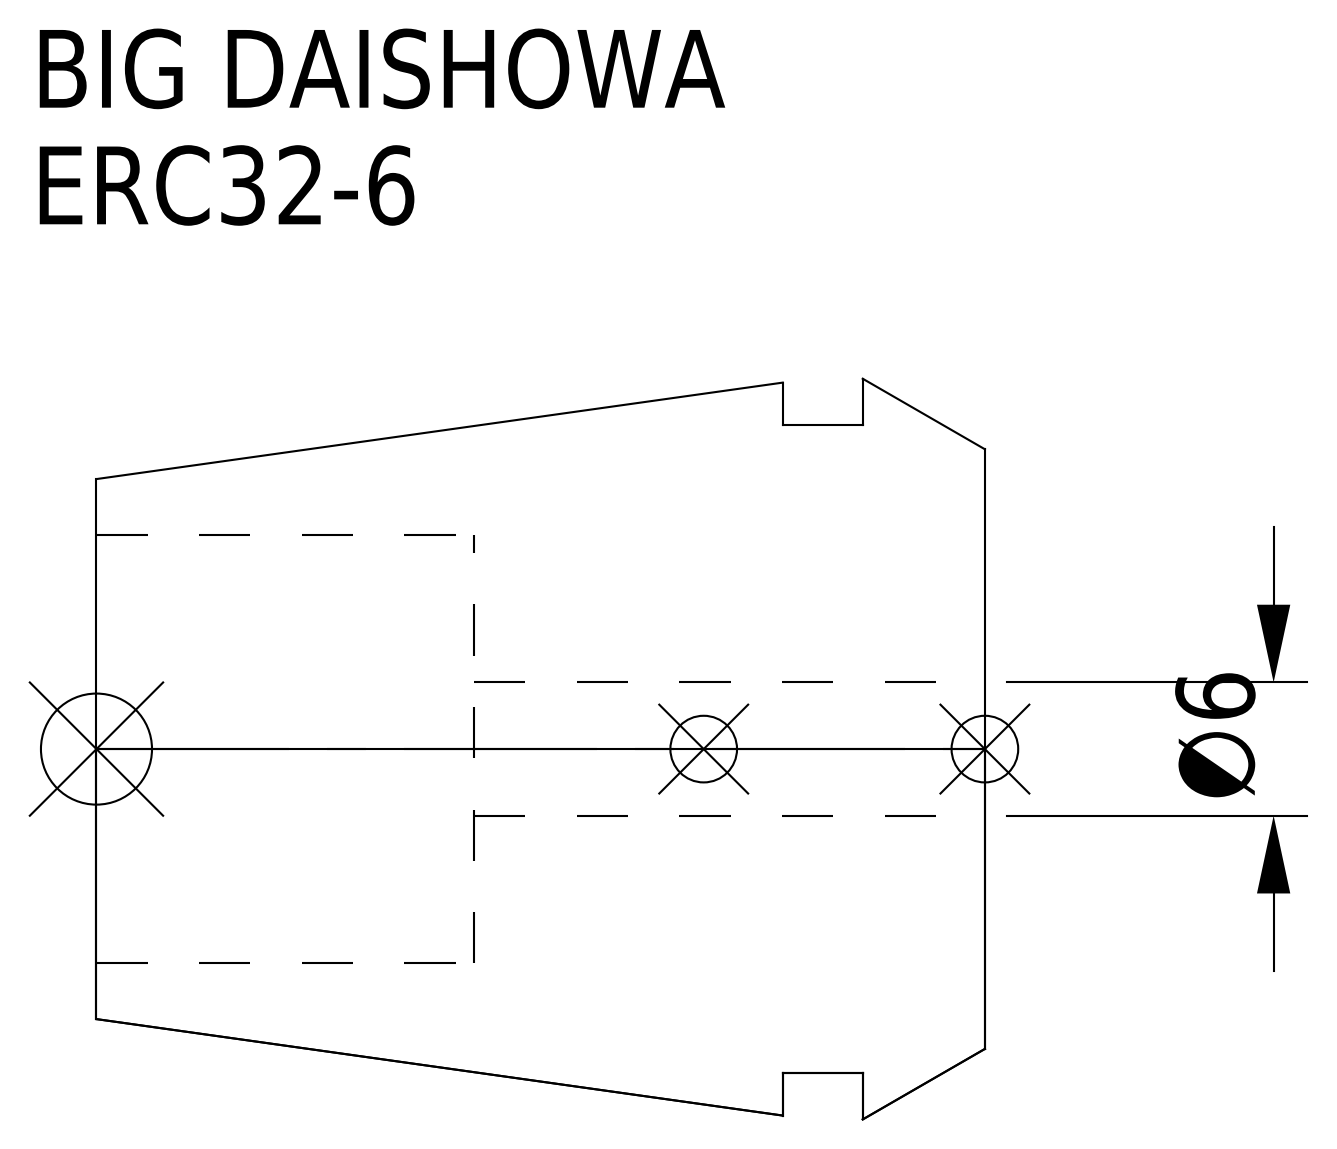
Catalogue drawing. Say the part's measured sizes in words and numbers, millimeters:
The part is named "ERC32-6". Its 3-D file was written by "CREO PARAMETRIC BY PTC INC, 2016380 (AUTOMOTIVE_DESIGN)". It is 1 solid with 15 faces: 5 planar, 6 cylindrical and 4 other. Overall it measures 40 by 33.35 by 33.35 millimeters. Its volume is 20 819 cubic millimeters and its surface area 6 576 square millimeters. Round holes: 1 of diameter 6, 1 of diameter 19.3. Round bosses or shafts: 1 of diameter 29.2. The main face-to-face distances are 23, 5.5, 17.5, 9.1, 3.6, 13.9, 40, 34.5, 30.9, 17.
